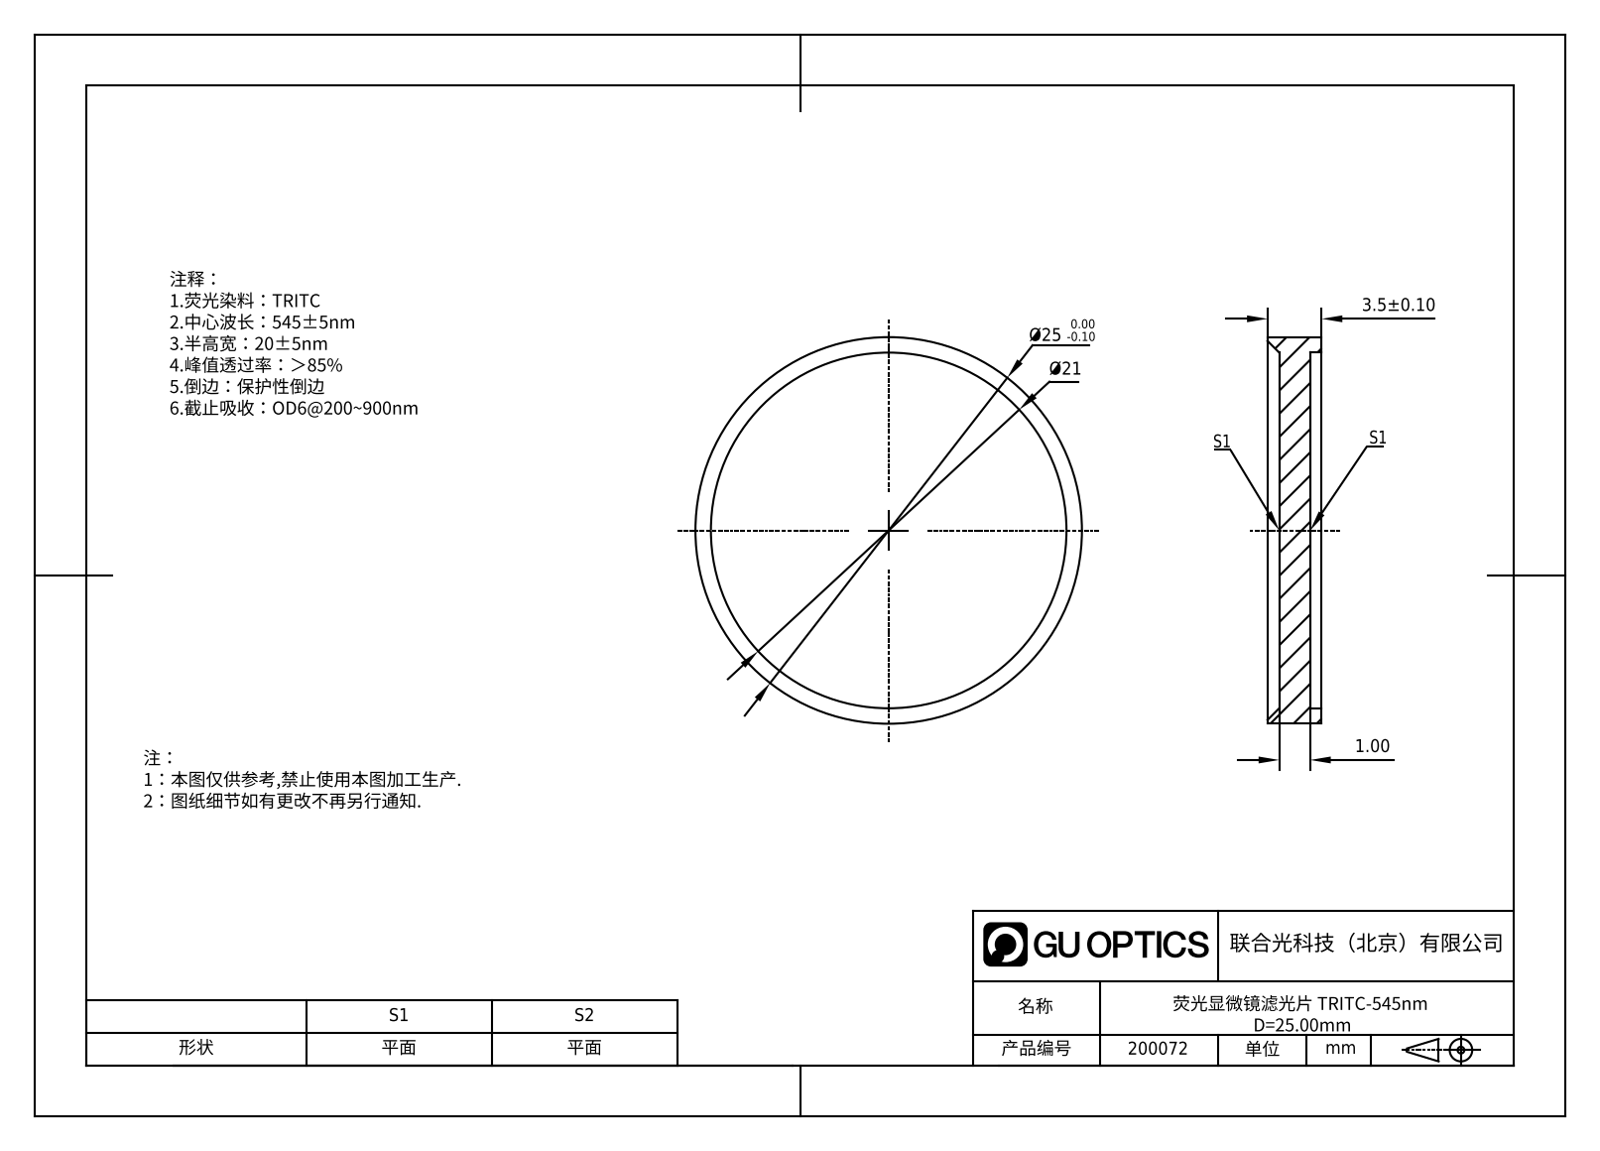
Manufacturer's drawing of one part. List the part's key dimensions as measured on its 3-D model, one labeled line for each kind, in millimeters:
Part name (STEP PRODUCT): GNIF-020-545-D25
STEP written by: SolidWorks 2022 (AUTOMOTIVE_DESIGN)
Units: millimetres
Bodies: 1 solid, 10 faces (4 planar, 4 cylindrical, 2 other)
Overall size (bounding box): 25 × 25 × 3.5
Volume: 1 074 mm³ · Surface area: 1 334 mm²
Round holes (diameter × count): ⌀23 ×1
Round bosses / shafts (diameter × count): ⌀25 ×1
Main face-to-face distances: 2, 0.75, 2.75, 3.5
